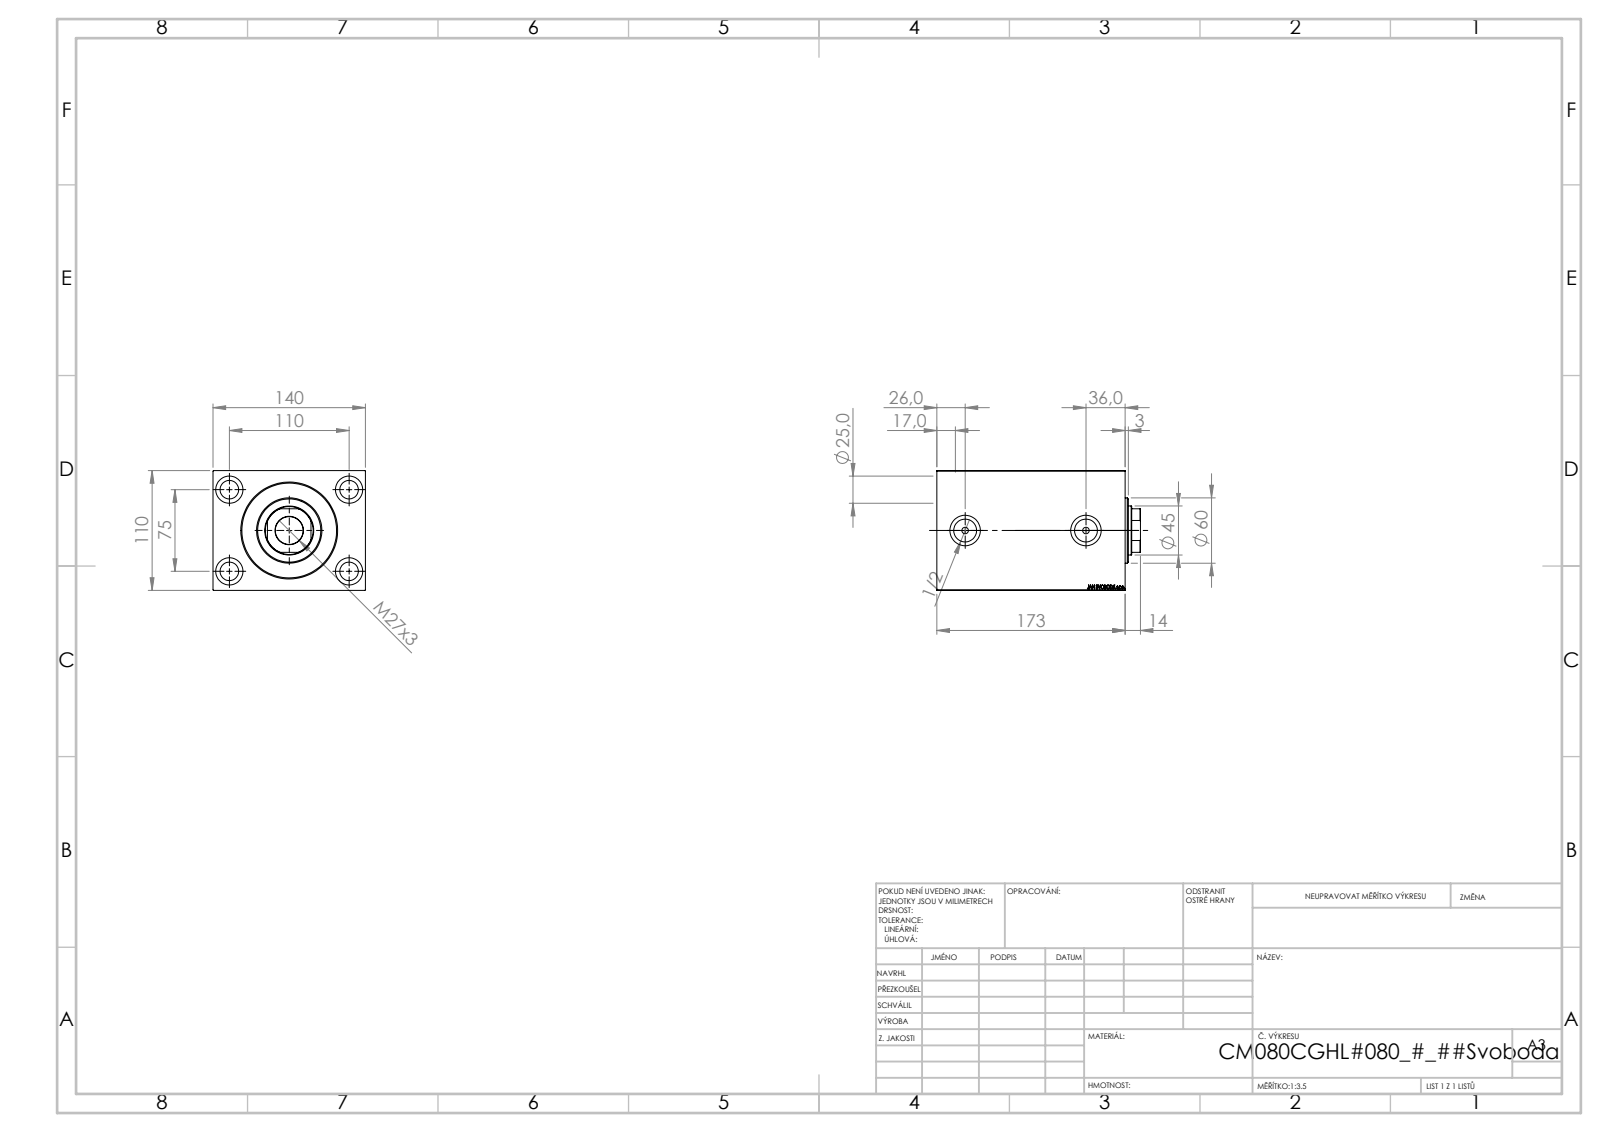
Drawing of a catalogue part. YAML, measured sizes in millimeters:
part_name: "V450CM_C_Body; V450CM_VC_B; V450CM_C_VCP"
step_written_by: "SolidWorks 2019 (CONFIG_CONTROL_DESIGN)"
units: millimeters
bodies: {solids: 3, faces: 862, planar: 408, cylindrical: 60, other: 394}
overall_size: [187, 140, 110]
volume: 2193000
surface_area: 253950
round_holes:
  - {diameter: 17, count: 4}
  - {diameter: 25, count: 4}
  - {diameter: 6, count: 2}
  - {diameter: 20.96, count: 2}
  - {diameter: 28, count: 2}
  - {diameter: 25.5, count: 1}
  - {diameter: 45, count: 1}
  - {diameter: 80, count: 1}
  - {diameter: 82, count: 1}
  - {diameter: 87, count: 1}
round_bosses_or_shafts:
  - {diameter: 60, count: 1}
partial_cylinders:
  - {radius: 22, count: 1}
face_to_face_distances: [110, 140, 173, 152, 21, 159, 14, 138, 94, 80]
hole_center_spacings: [66.57, 75, 110, 133.14, 111]
